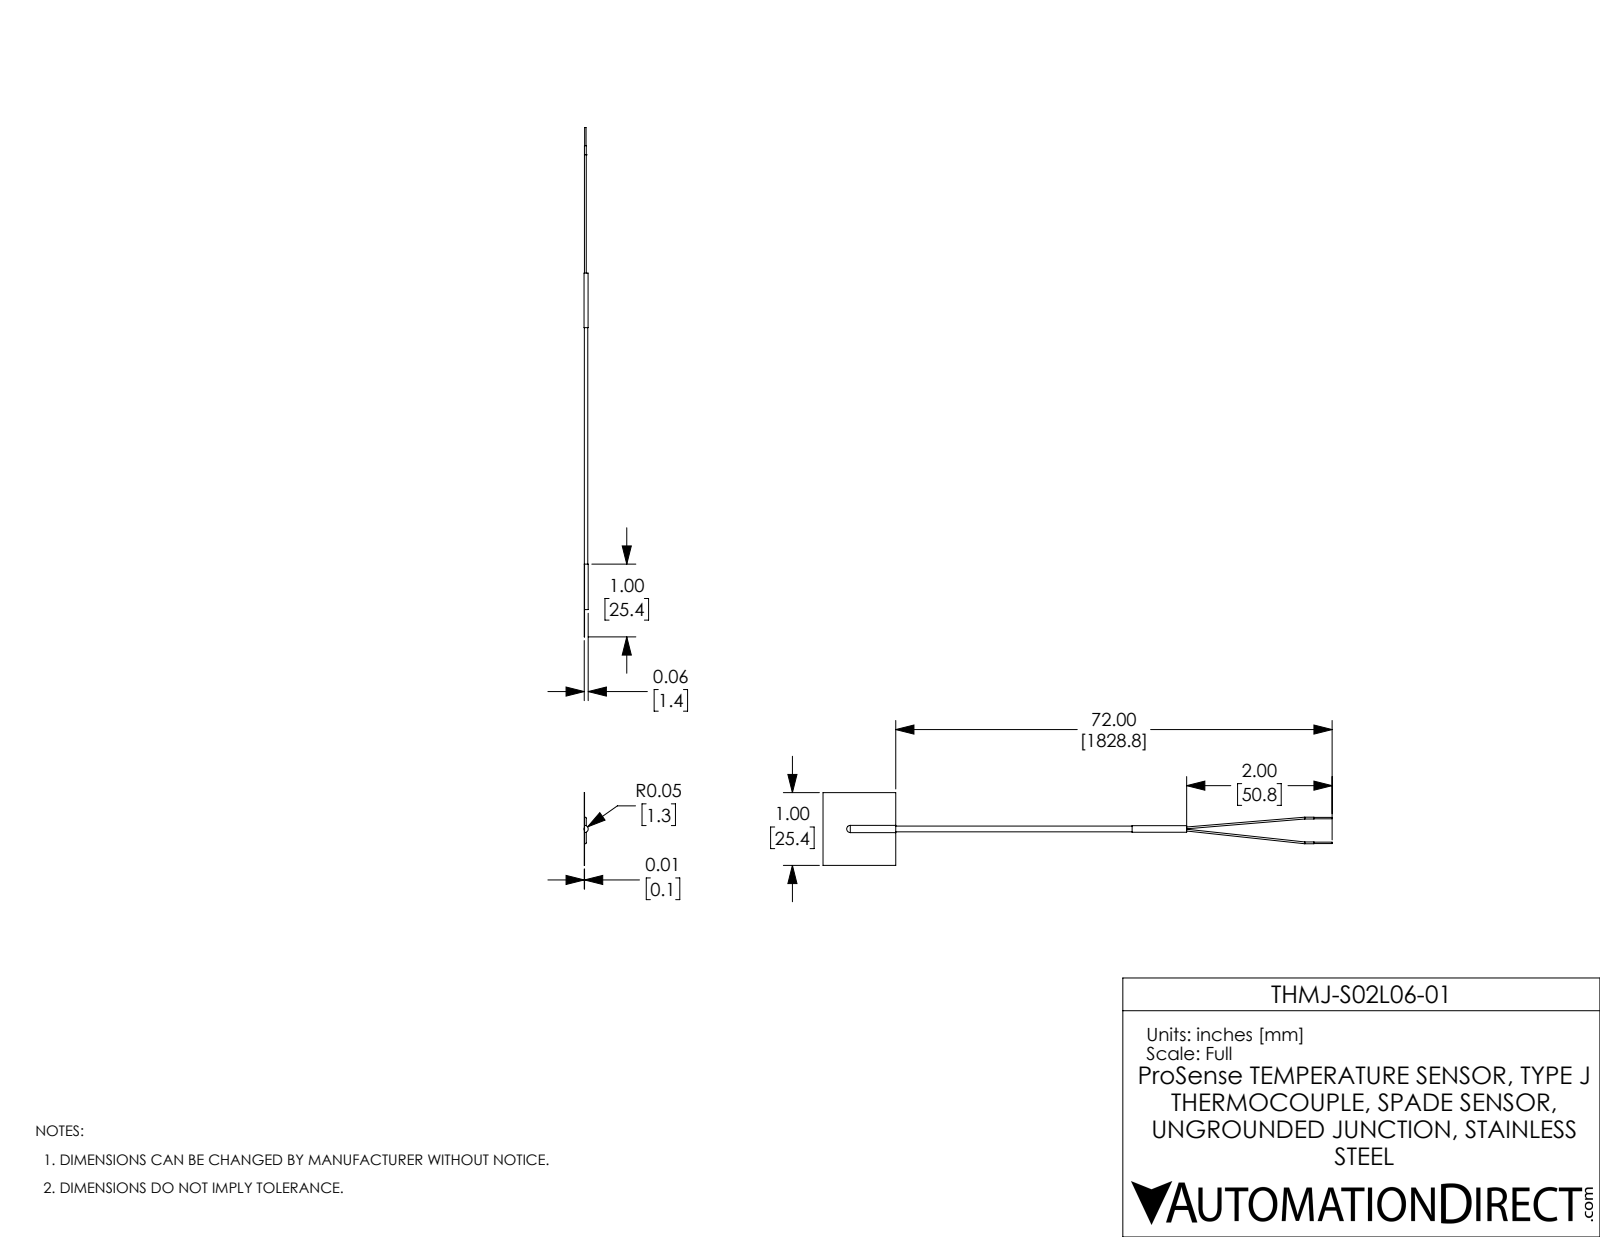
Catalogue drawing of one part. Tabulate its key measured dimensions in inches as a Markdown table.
| quantity | value |
| --- | --- |
| part name | THMJ-S02L06-01 |
| STEP written by | SolidWorks 2017 (AUTOMOTIVE_DESIGN) |
| units | inches |
| bodies | 3 solids, 37 faces (14 planar, 14 cylindrical, 9 other) |
| overall size | 7 × 1 × 0.057 |
| volume | 0.023 in³ |
| surface area | 3.29 in² |
| round bosses / shafts (diameter × count) | 0.025 × 4, 0.02 × 2 |
| partial cylindrical surfaces (radius × count) | 0.05 × 1 |
| main face-to-face distances | 1, 4, 5, 0.25, 0.5, 3.5, 4.5, 2.5, 0.75, 3.25 |
